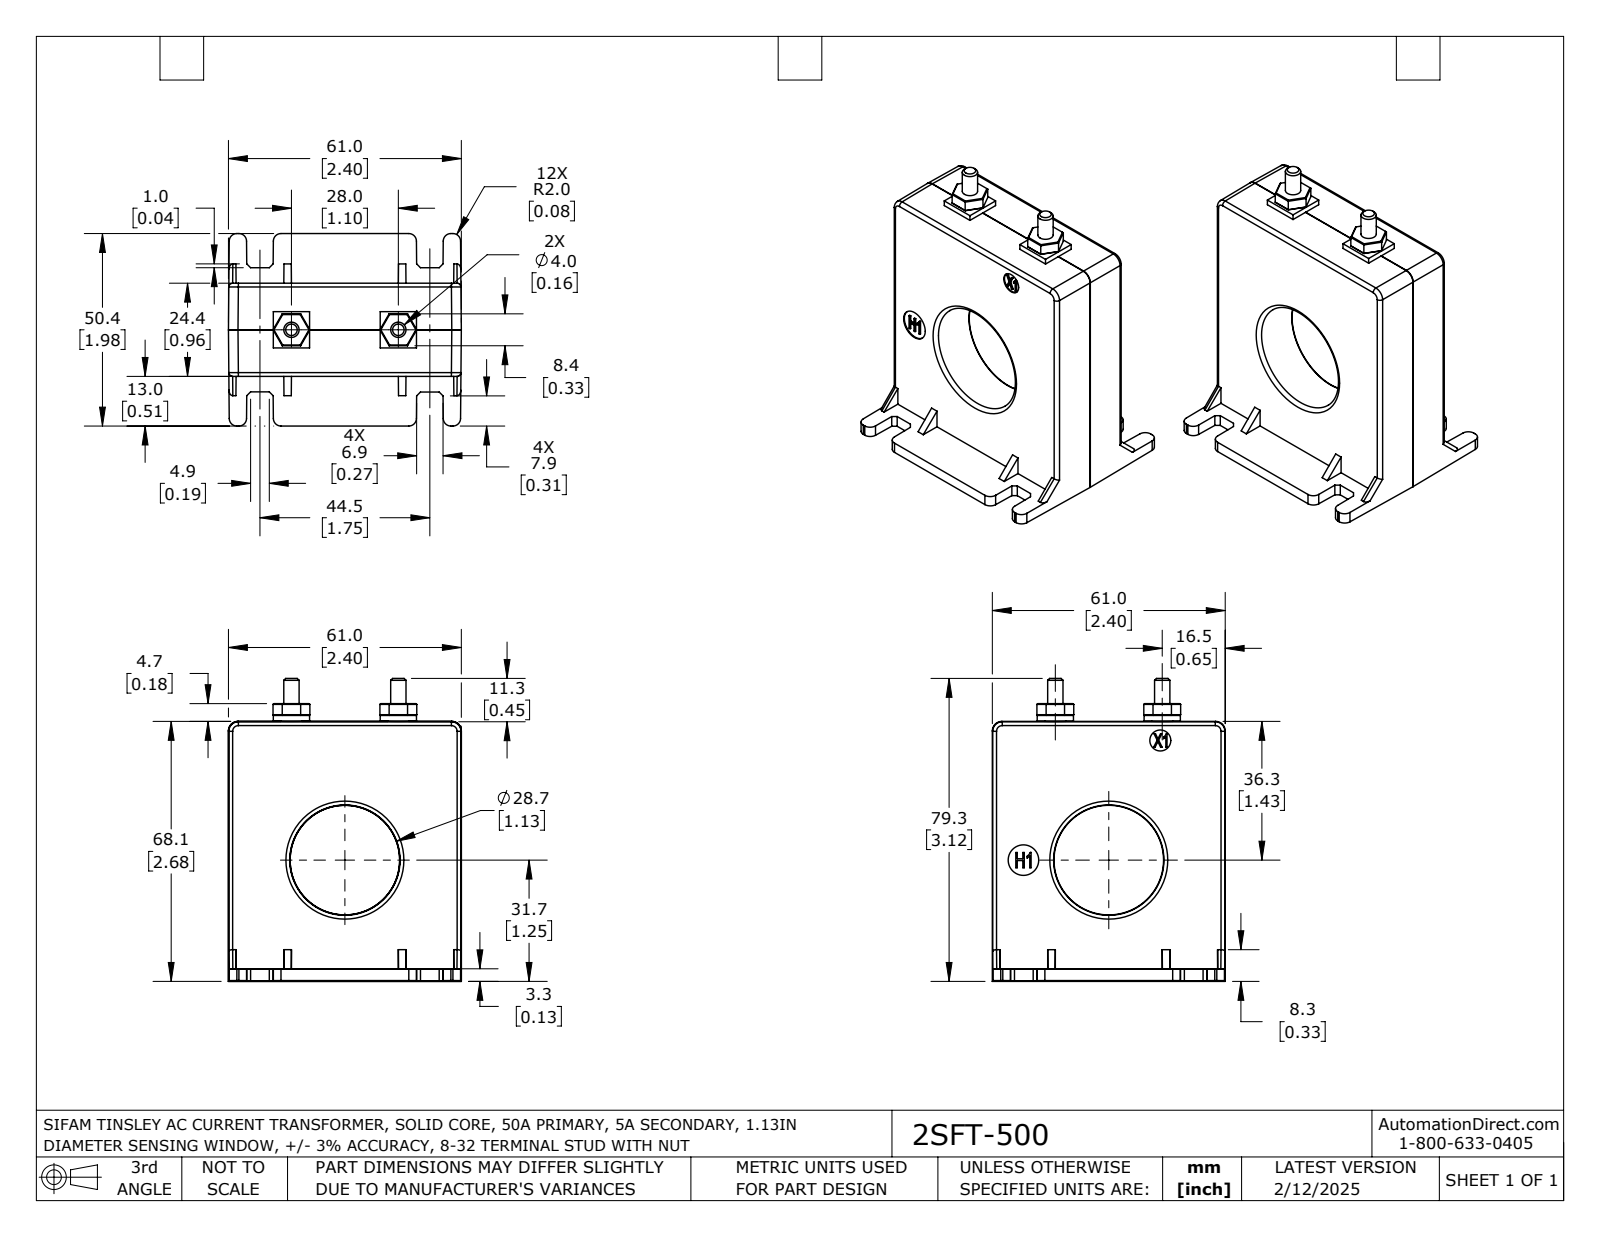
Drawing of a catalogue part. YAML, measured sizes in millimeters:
part_name: "2SFT-500"
step_written_by: "SolidWorks 2021 (AUTOMOTIVE_DESIGN)"
units: millimeters
bodies: {solids: 1, faces: 245, planar: 183, cylindrical: 38, other: 24}
overall_size: [79.3, 61, 50.4]
volume: 89620
surface_area: 25850
round_holes:
  - {diameter: 5.5, count: 1}
  - {diameter: 8, count: 1}
round_bosses_or_shafts:
  - {diameter: 5.5, count: 2}
  - {diameter: 4, count: 2}
partial_cylinders:
  - {radius: 2, count: 12}
  - {radius: 1, count: 10}
  - {radius: 2.5, count: 4}
face_to_face_distances: [12.2, 12.1, 12.3, 24.4, 61, 3.4, 68.1, 64.7, 13, 25.2]
hole_center_spacings: [47.6]
